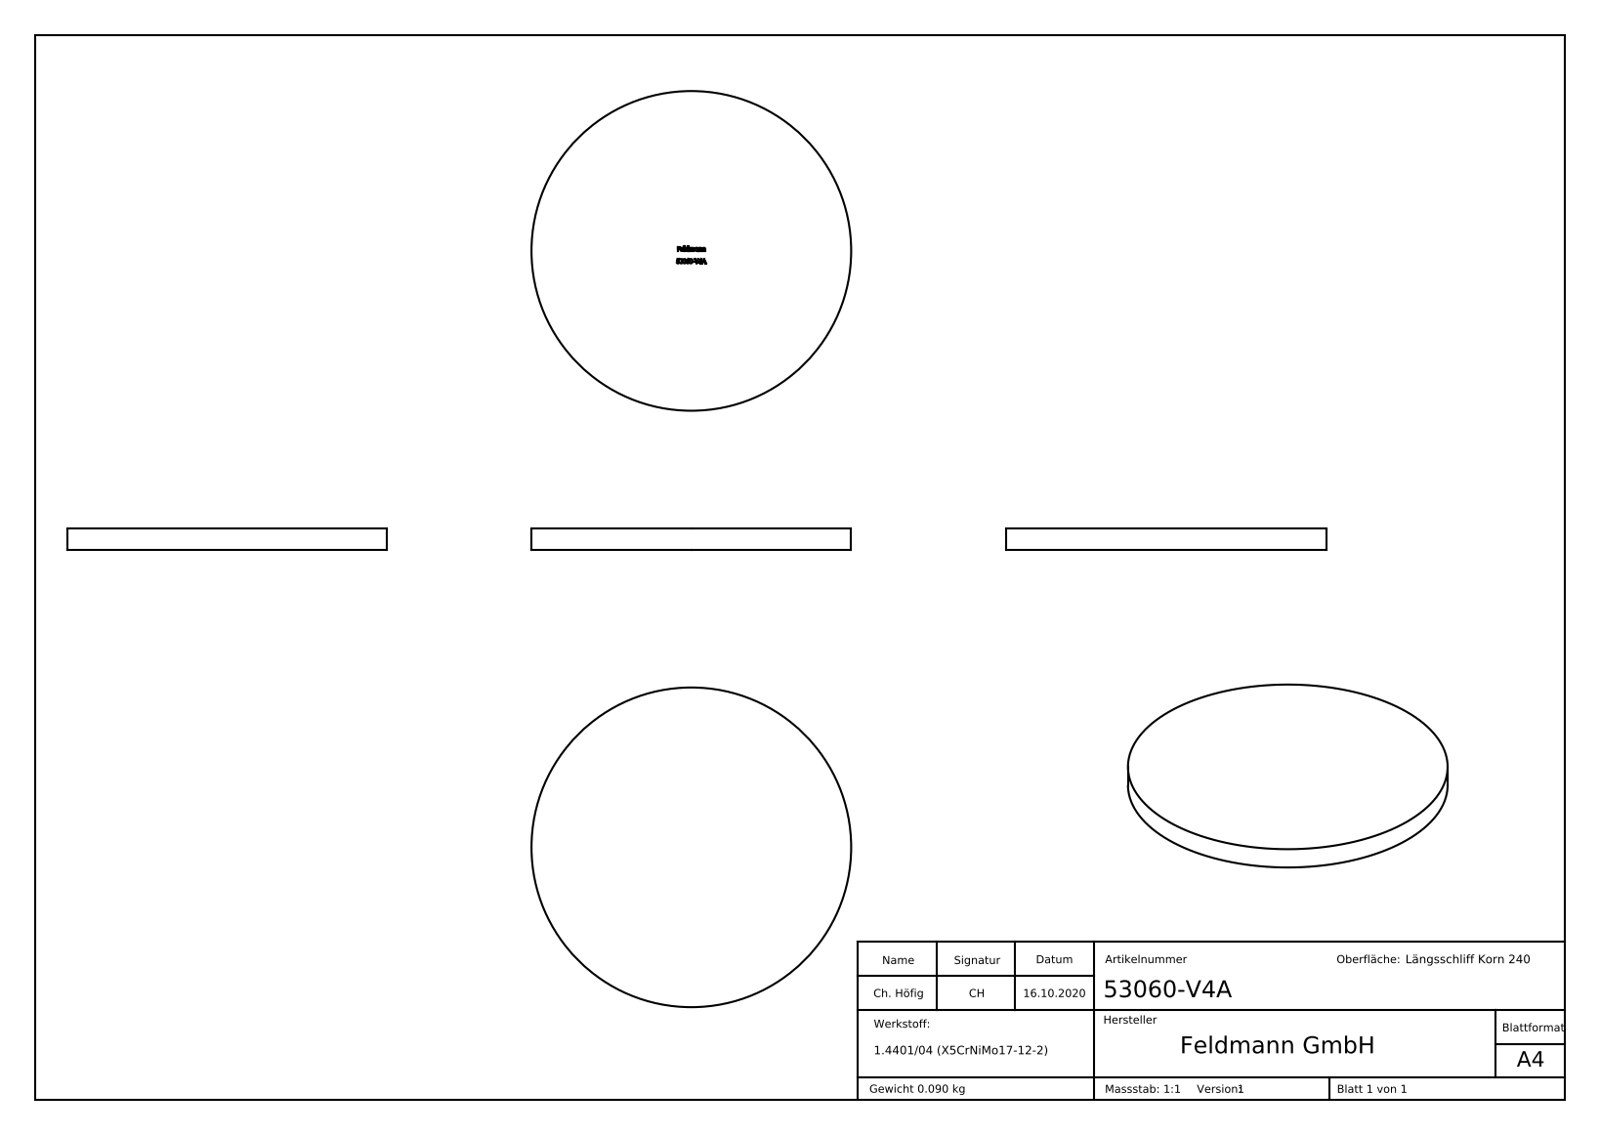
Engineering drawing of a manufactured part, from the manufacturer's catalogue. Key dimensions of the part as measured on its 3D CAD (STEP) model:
Part name (STEP PRODUCT): 53060-V4A
STEP written by: SolidWorks 2018 (CONFIG_CONTROL_DESIGN)
Units: millimetres
Bodies: 1 solid, 227 faces (128 planar, 2 cylindrical, 97 other)
Overall size (bounding box): 60 × 60 × 4
Volume: 11 310 mm³ · Surface area: 6 415 mm²
Round bosses / shafts (diameter × count): ⌀60 ×1
Main face-to-face distances: 4, 3.9, 1.78, 0.44, 2.45, 0.83, 0.99, 2.77, 2.38, 0.67
